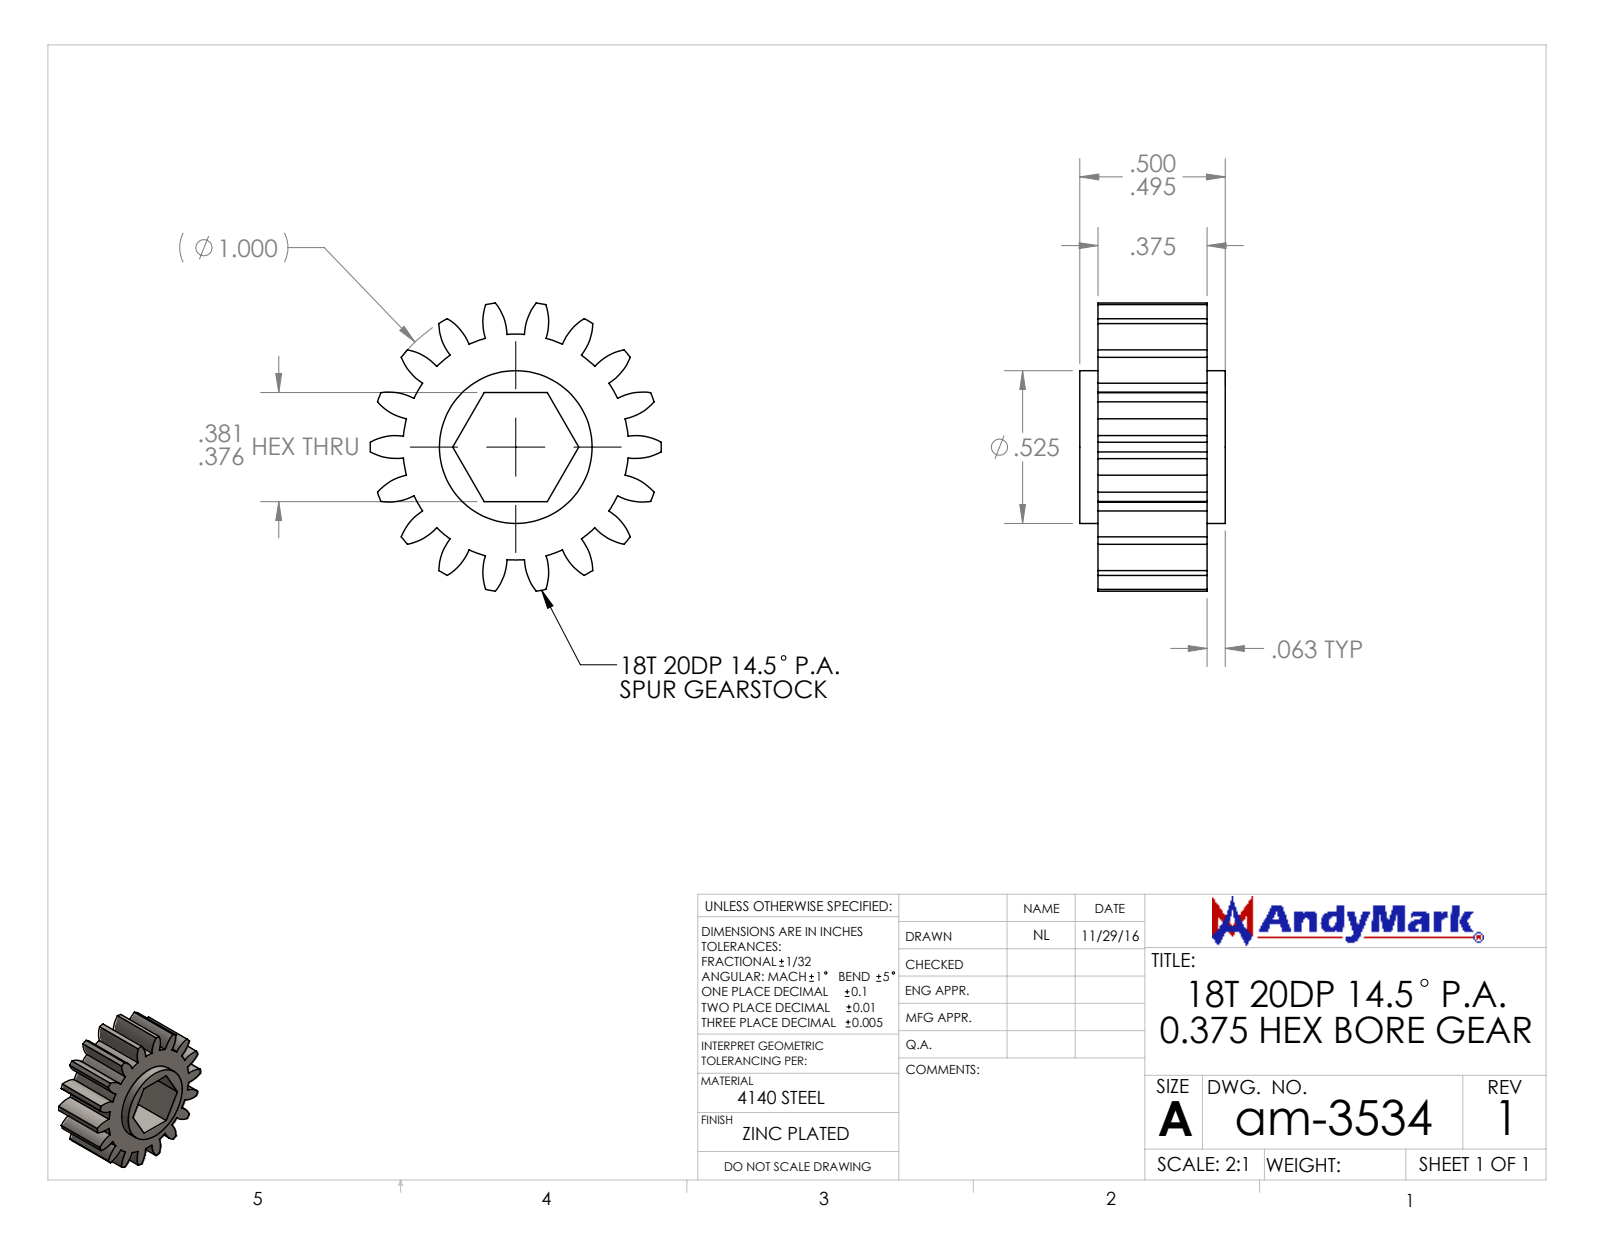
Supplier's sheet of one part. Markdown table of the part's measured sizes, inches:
| quantity | value |
| --- | --- |
| part name | am-3534 18T 20DP 375hex 375 FW |
| STEP written by | SolidWorks 2014 (AUTOMOTIVE_DESIGN) |
| units | inches |
| bodies | 1 solid, 89 faces (10 planar, 79 cylindrical, 0 other) |
| overall size | 1 × 0.99 × 0.5 |
| volume | 0.194 in³ |
| surface area | 4.05 in² |
| round bosses / shafts (diameter × count) | 0.525 × 1 |
| partial cylindrical surfaces (radius × count) | 0.18 × 36, 0.388 × 1, 0.5 × 1 |
| main face-to-face distances | 0.375, 0.375, 0.063, 0.438, 0.5, 0.437, 0.062 |
